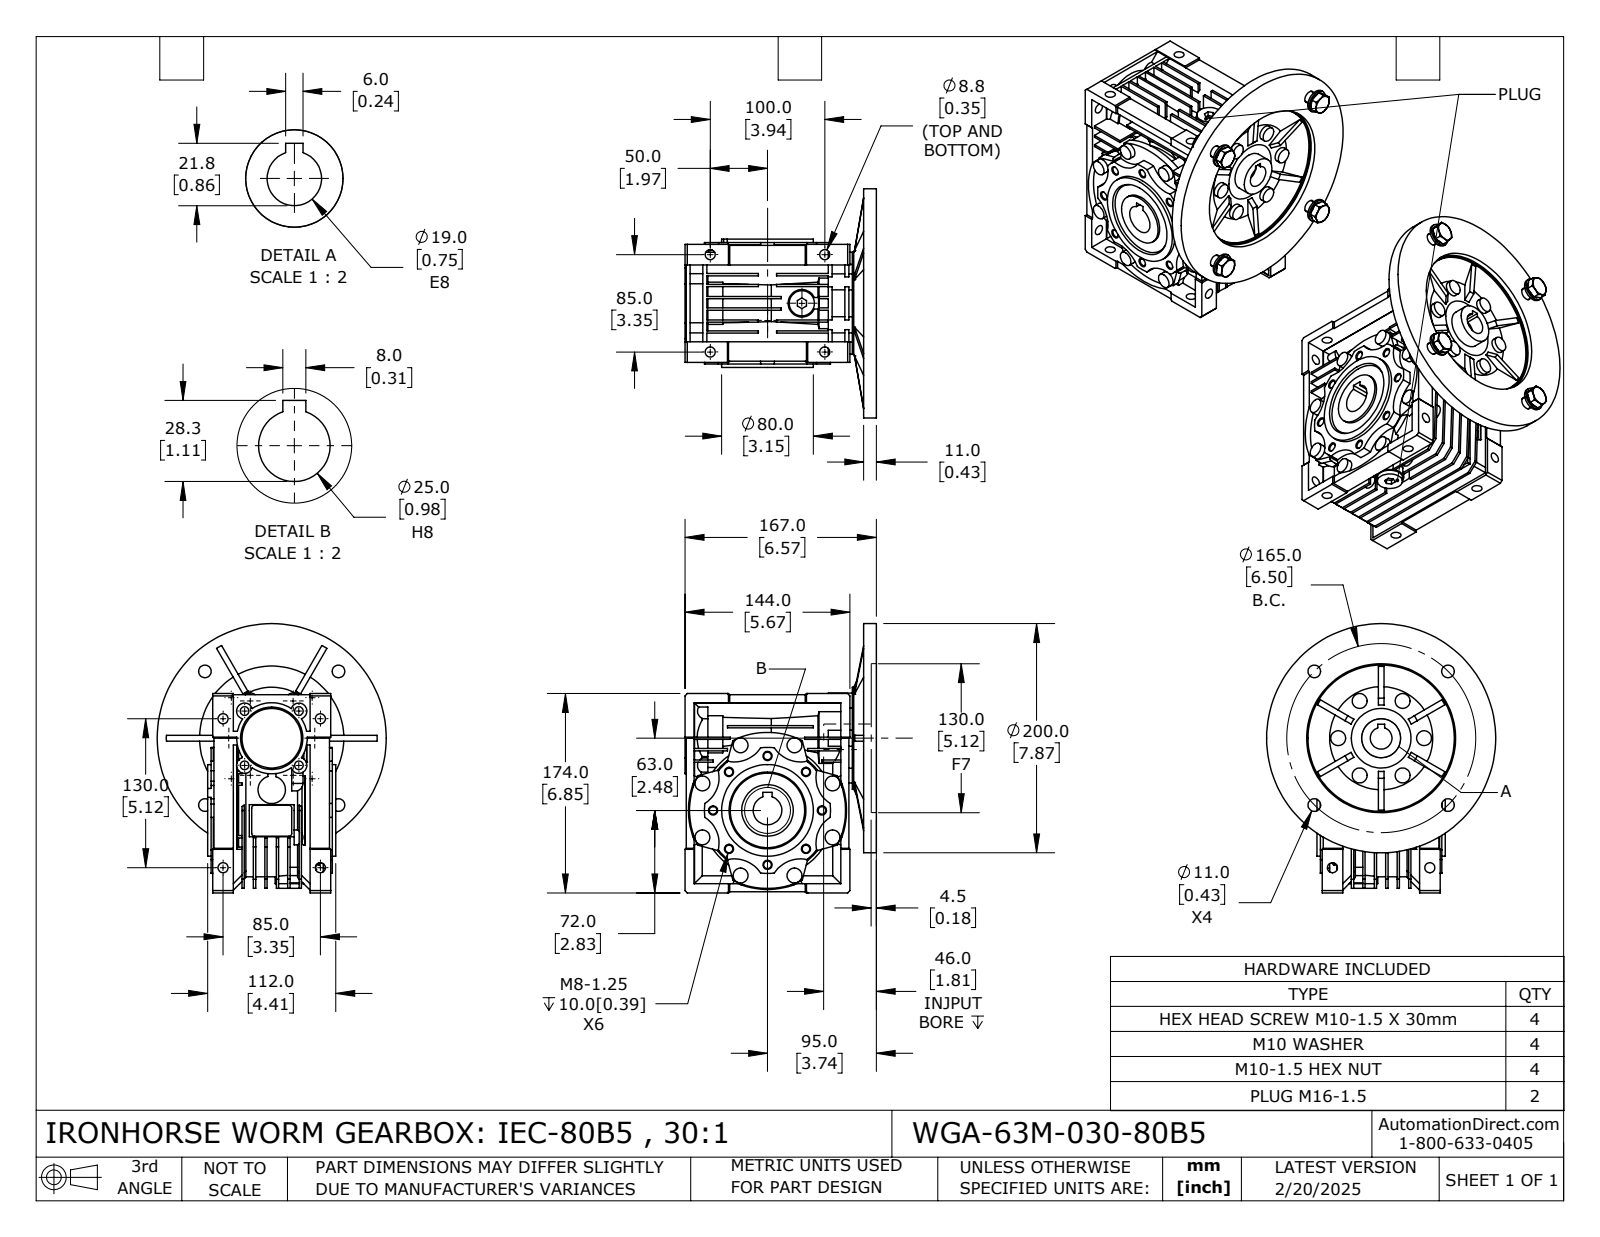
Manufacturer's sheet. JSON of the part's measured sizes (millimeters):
{"part_name": "WGA-63M-030-80B5", "step_written_by": "SolidWorks 2024 (CONFIG_CONTROL_DESIGN)", "units": "millimeters", "bodies": {"solids": 20, "faces": 1529, "planar": 897, "cylindrical": 394, "other": 238}, "overall_size": [235, 200, 183.43], "volume_mm3": 2032000, "surface_area_mm2": 401437, "round_holes": [[6.65, 8], [8.78, 8], [7.56, 4], [8.5, 4], [10, 4], [10.5, 4], [11, 4], [14.5, 2], [19, 1], [20, 1], [25, 1], [34, 1]], "round_bosses_or_shafts": [[13, 14], [20, 4], [16, 4], [24, 3], [22, 2], [15.8, 2], [13.7, 2], [200, 1]], "partial_cylinders_radius": [[7, 10], [27, 8], [2.5, 4], [8.35, 1], [29.5, 1], [30.5, 1], [42, 1], [46, 1]], "face_to_face_distances": [10, 8, 20, 2, 11, 30, 12, 7, 40, 18], "hole_center_spacings": [36.36, 47.5, 67.18, 87.77, 89.05, 33.5, 47.38, 49]}
